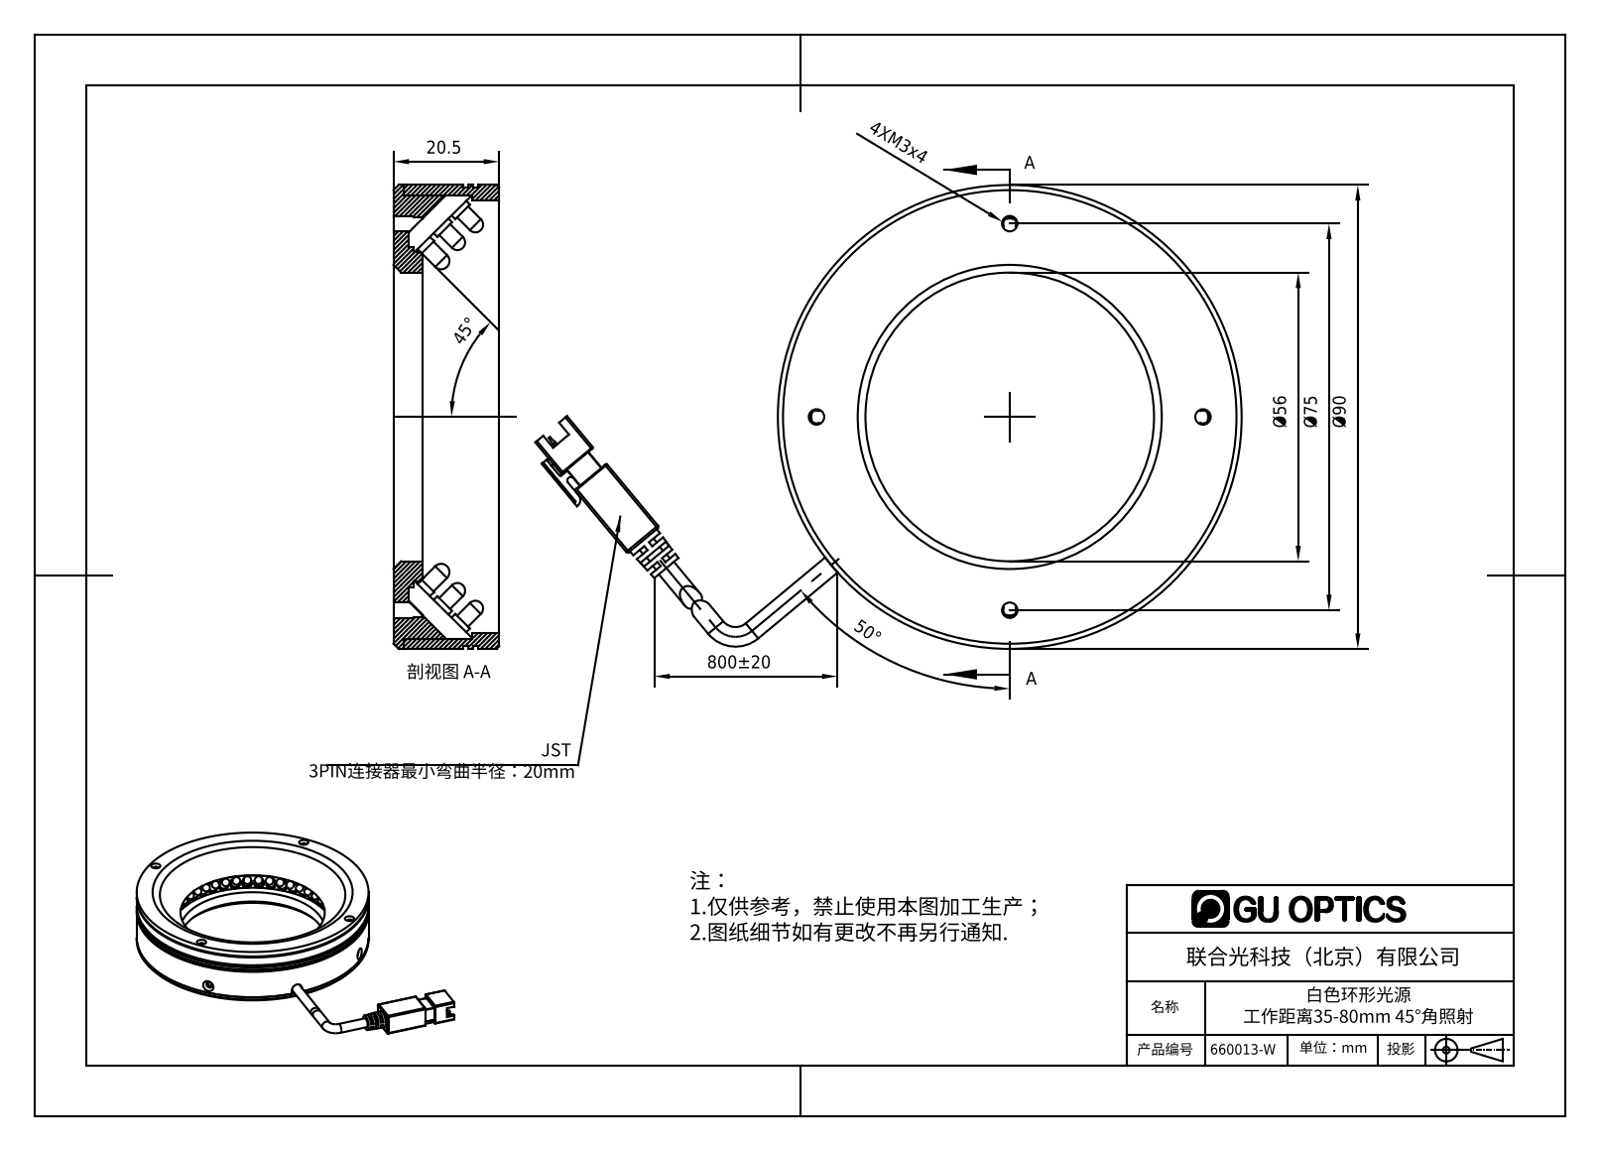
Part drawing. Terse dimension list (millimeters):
name: 660013-W
written by: SolidWorks 2016 (AUTOMOTIVE_DESIGN)
unit: mm
bodies: 156 solids, 2970 faces (1958 planar, 768 cylindrical, 244 other)
size: 141.36 × 95.39 × 24.5
volume: 48 891 mm³; area: 57 279 mm²
holes: 4× ⌀1.25, 4× ⌀1.6, 4× ⌀1.8, 4× ⌀2, 4× ⌀3, 3× ⌀3.5, 2× ⌀2.4, 1× ⌀56, 1× ⌀84
bosses: 150× ⌀3.8, 150× ⌀3, 2× ⌀3.5, 1× ⌀90, 1× ⌀89, 1× ⌀86, 1× ⌀66, 1× ⌀63.8
rounds: 15× R0.1, 13× R0.2, 12× R0.4, 4× R1.25, 1× R0.3, 1× R0.68, 1× R1.4, 1× R1.6
face distances: 2, 20.5, 1, 22.5, 18.5, 3, 14.8, 3.7, 5.7, 16.8
hole spacings: 56.68, 3.99, 5, 6.64, 37.5, 42.5, 53.03, 60.1
